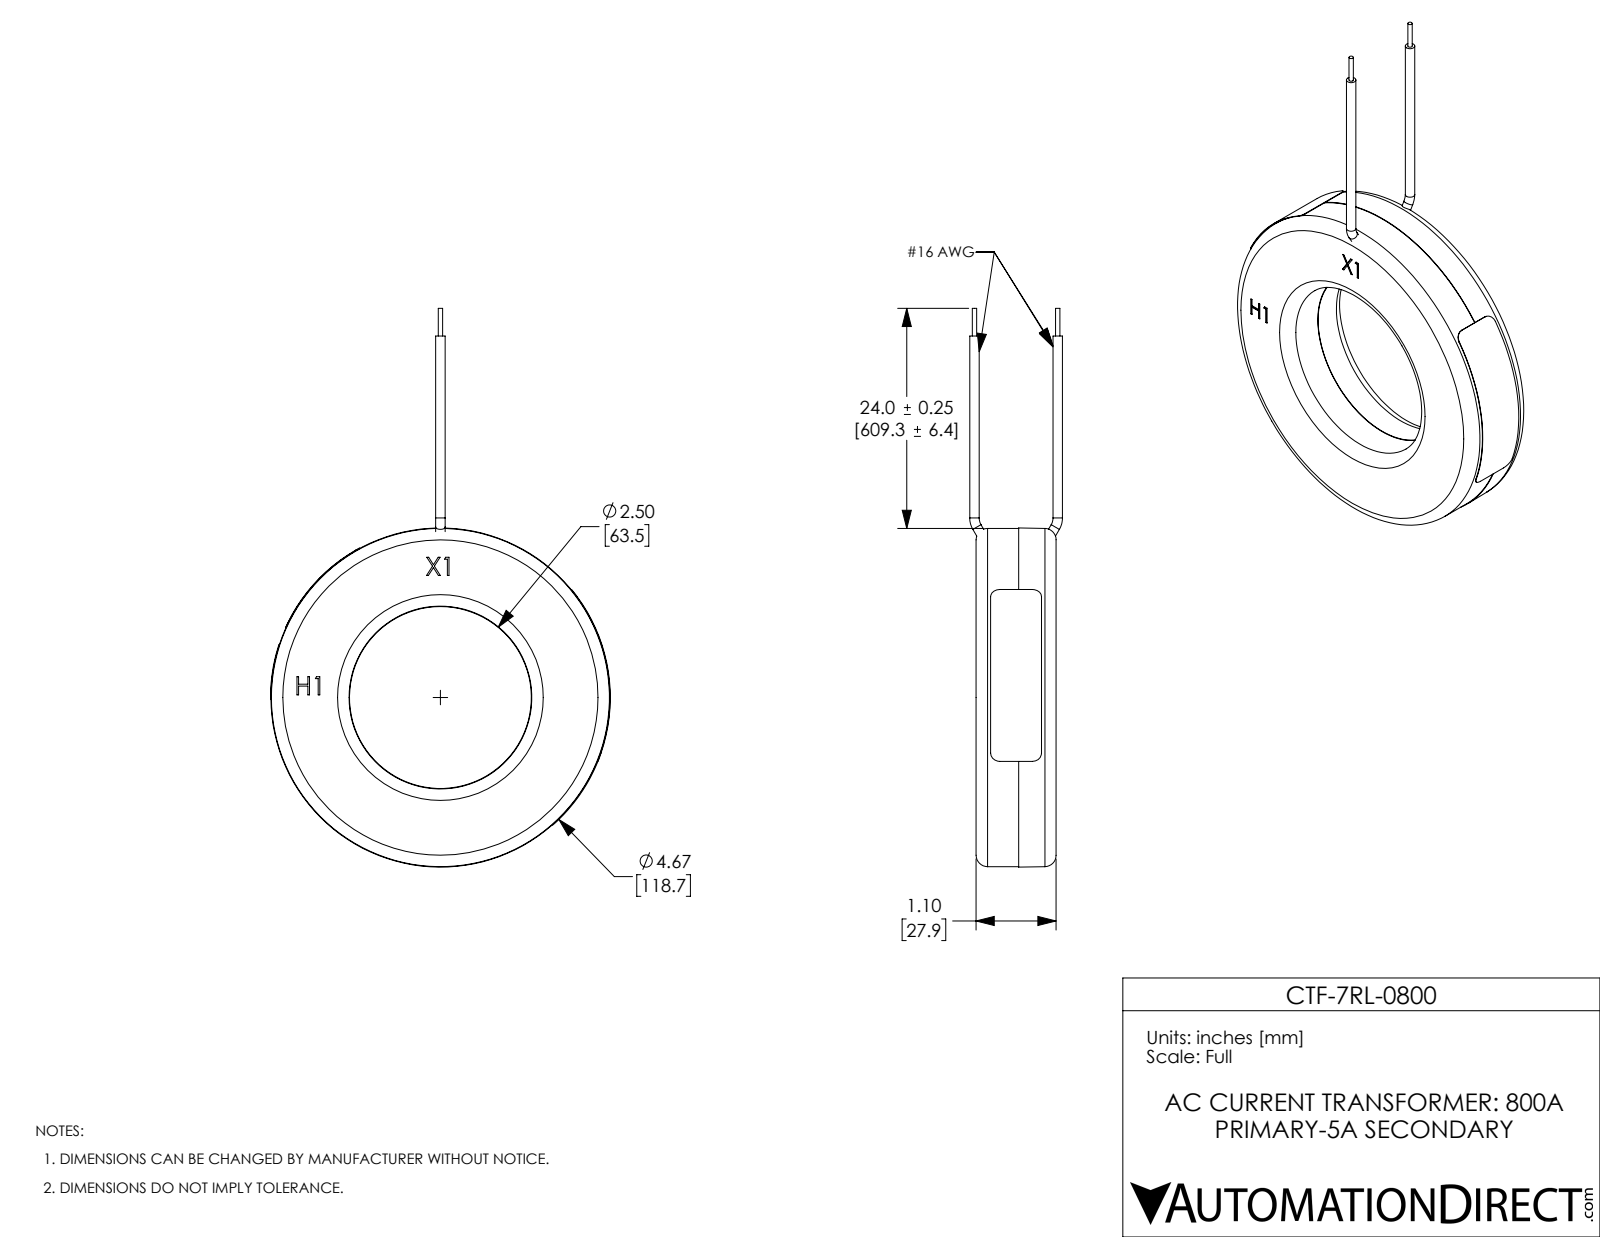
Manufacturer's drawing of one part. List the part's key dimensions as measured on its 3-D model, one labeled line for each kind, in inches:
Part name (STEP PRODUCT): CTF-7RL-0800
STEP written by: SolidWorks 2018 (AUTOMOTIVE_DESIGN)
Units: inches
Bodies: 6 solids, 114 faces (62 planar, 31 cylindrical, 21 other)
Overall size (bounding box): 7.679 × 4.673 × 1.275
Volume: 13.1 in³ · Surface area: 79.58 in²
Round holes (diameter × count): ⌀2.513 ×1
Round bosses / shafts (diameter × count): ⌀0.13 ×4, ⌀0.06 ×2, ⌀4.648 ×1
Partial cylindrical surfaces — rounded edges, fillets, slot ends (radius × count): R0.06 ×4, R0.125 ×4, R2.33 ×1, R2.33 ×1, R2.331 ×1, R2.336 ×1
Main face-to-face distances: 0.515, 1.1, 0.585, 1.09, 0.575, 0.2, 0.9, 0.315, 0.89, 0.7
